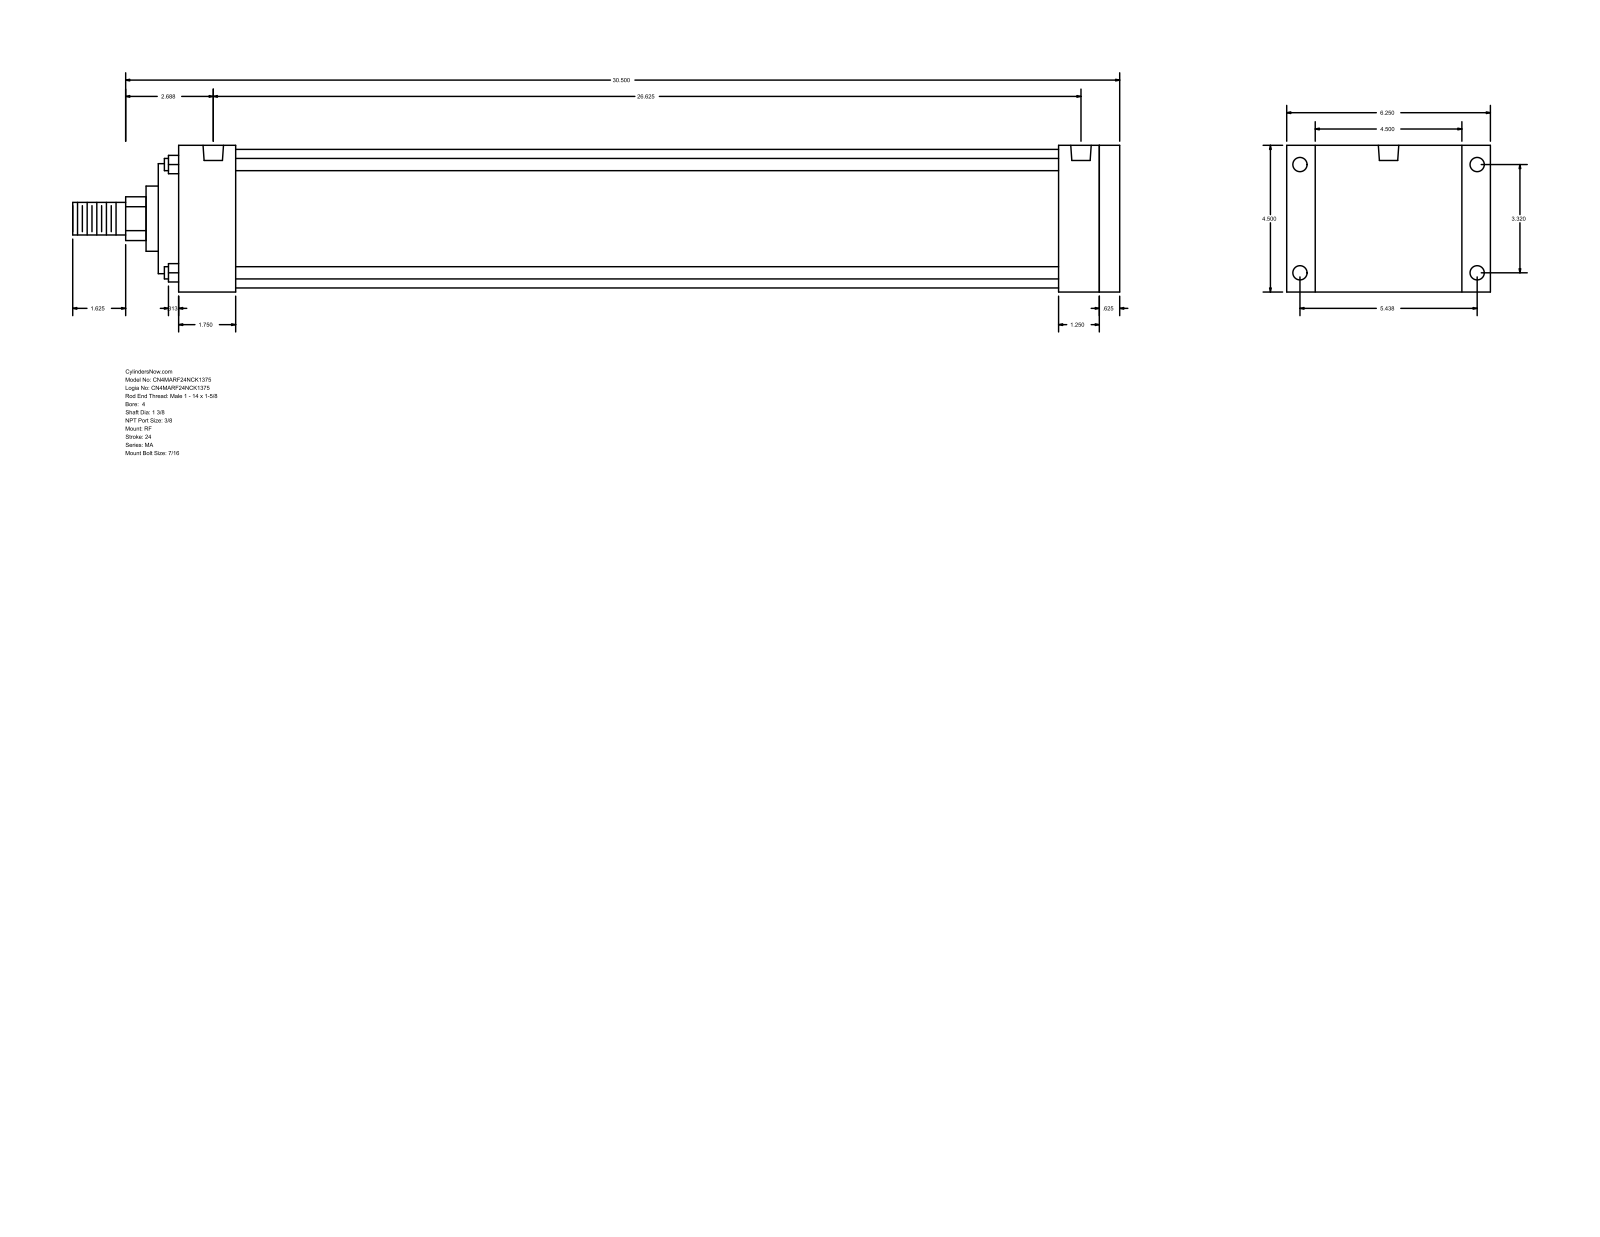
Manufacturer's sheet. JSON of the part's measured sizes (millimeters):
{"part_name": "MA_RF__0400_1.375", "step_written_by": "GSSL Pune (CONFIG_CONTROL_DESIGN)", "units": "millimeters", "bodies": {"solids": 0, "faces": 94, "planar": 65, "cylindrical": 29, "other": 0}, "overall_size": [815.98, 158.75, 114.3], "round_holes": [[11.11, 8], [15.93, 2]], "round_bosses_or_shafts": [[9.53, 4], [107.95, 1], [85.72, 1], [50.8, 1], [34.92, 1], [25.4, 1]], "partial_cylinders_radius": [[17.06, 1]], "face_to_face_distances": [114.3, 733.43, 15.87, 717.56, 749.3, 22.23, 136.53, 701.68, 685.81, 31.75], "hole_center_spacings": [4.77, 84.32, 138.12, 161.82, 666.74, 671.51, 676.28]}
